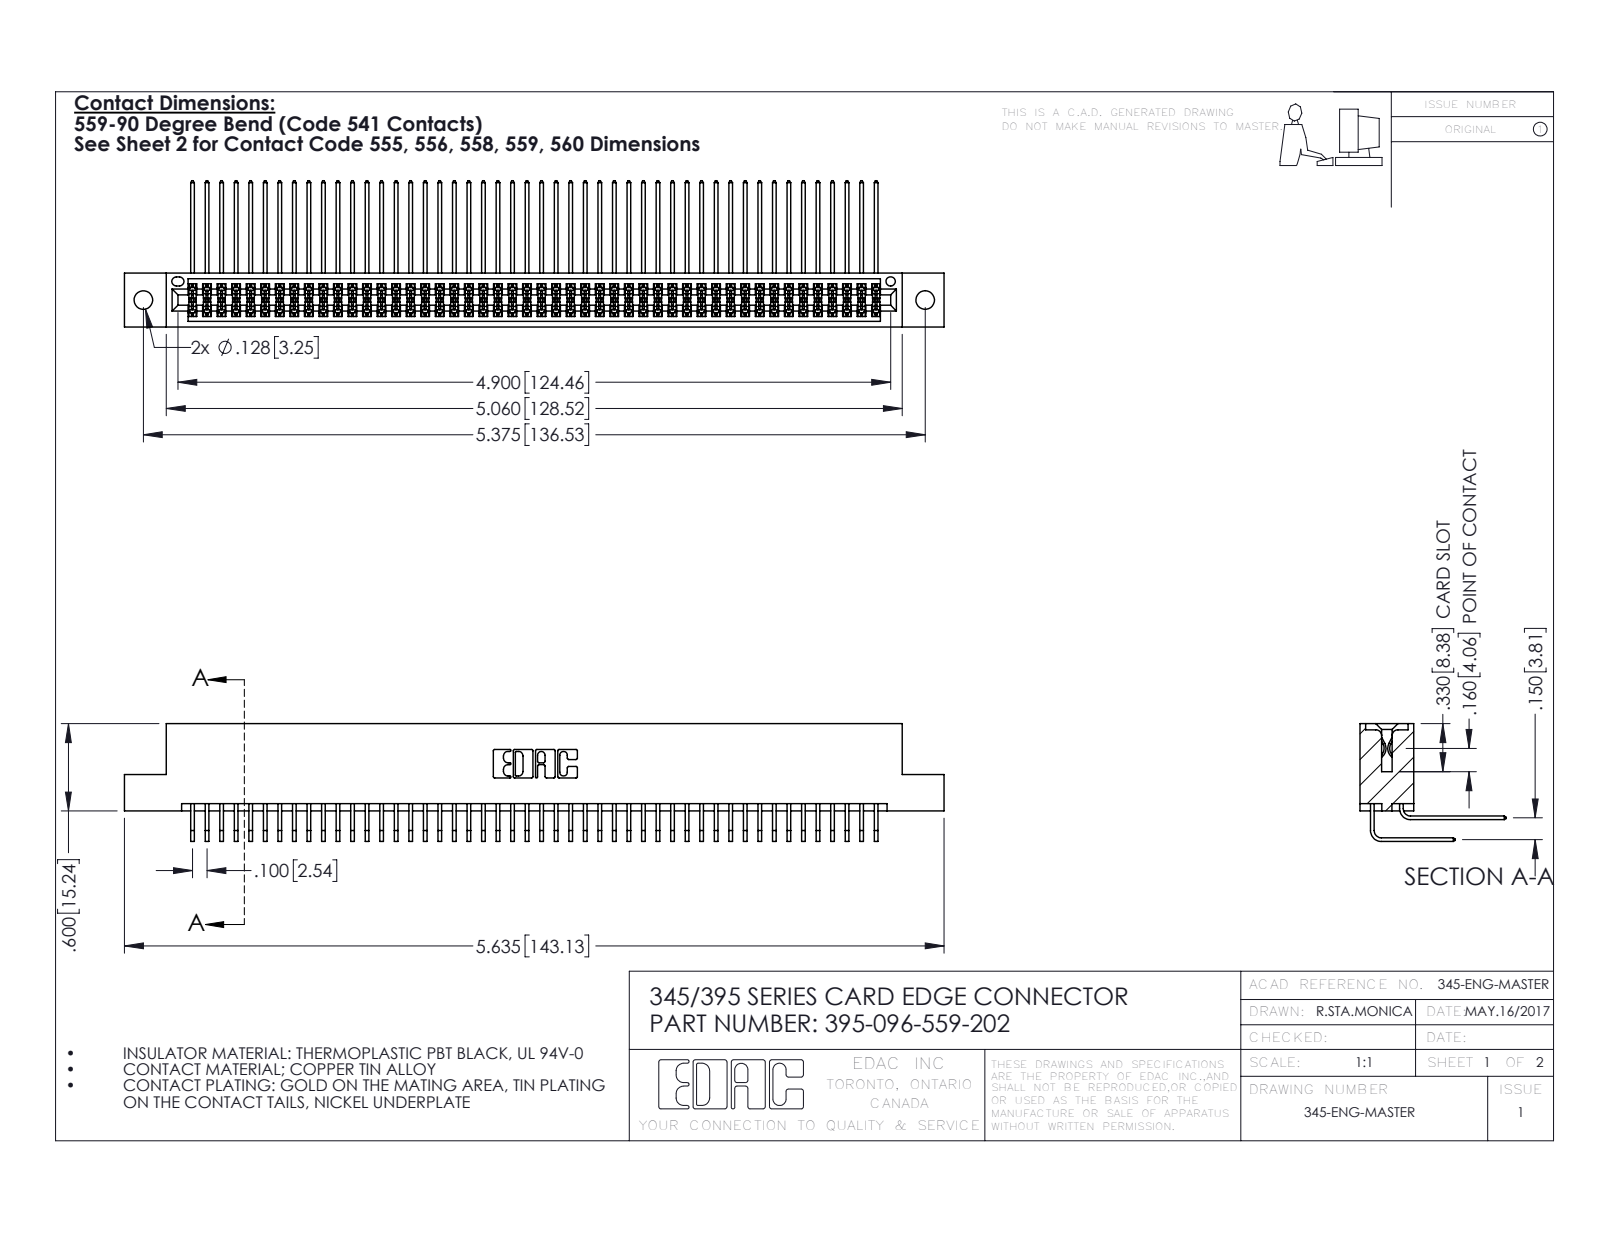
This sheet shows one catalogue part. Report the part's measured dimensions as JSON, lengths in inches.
{"part_name": "395-096-559-202; 345-292-001_558 559 Tail - 1; 345-292-001_559 Tail - 2; 345 Part_Flush Mounting Lugs - 0.128 Dia", "step_written_by": "SolidWorks 2016 (CONFIG_CONTROL_DESIGN)", "units": "inches", "bodies": {"solids": 97, "faces": 5118, "planar": 3440, "cylindrical": 1678, "other": 0}, "overall_size": [5.635, 1.005, 0.809], "volume_in3": 0.883, "surface_area_in2": 36.96, "round_holes": [[0.128, 2], [0.064, 1]], "partial_cylinders_radius": [[0.006, 145], [0.01, 22], [0.007, 6], [0.031, 6], [0.026, 3], [0.014, 2], [0.019, 2], [0.022, 2]], "face_to_face_distances": [0.072, 0.298, 0.2, 0.37, 0.098, 0.272, 0.025, 0.225, 0.175, 0.15], "hole_center_spacings": [0.27, 5.139, 5.375]}
